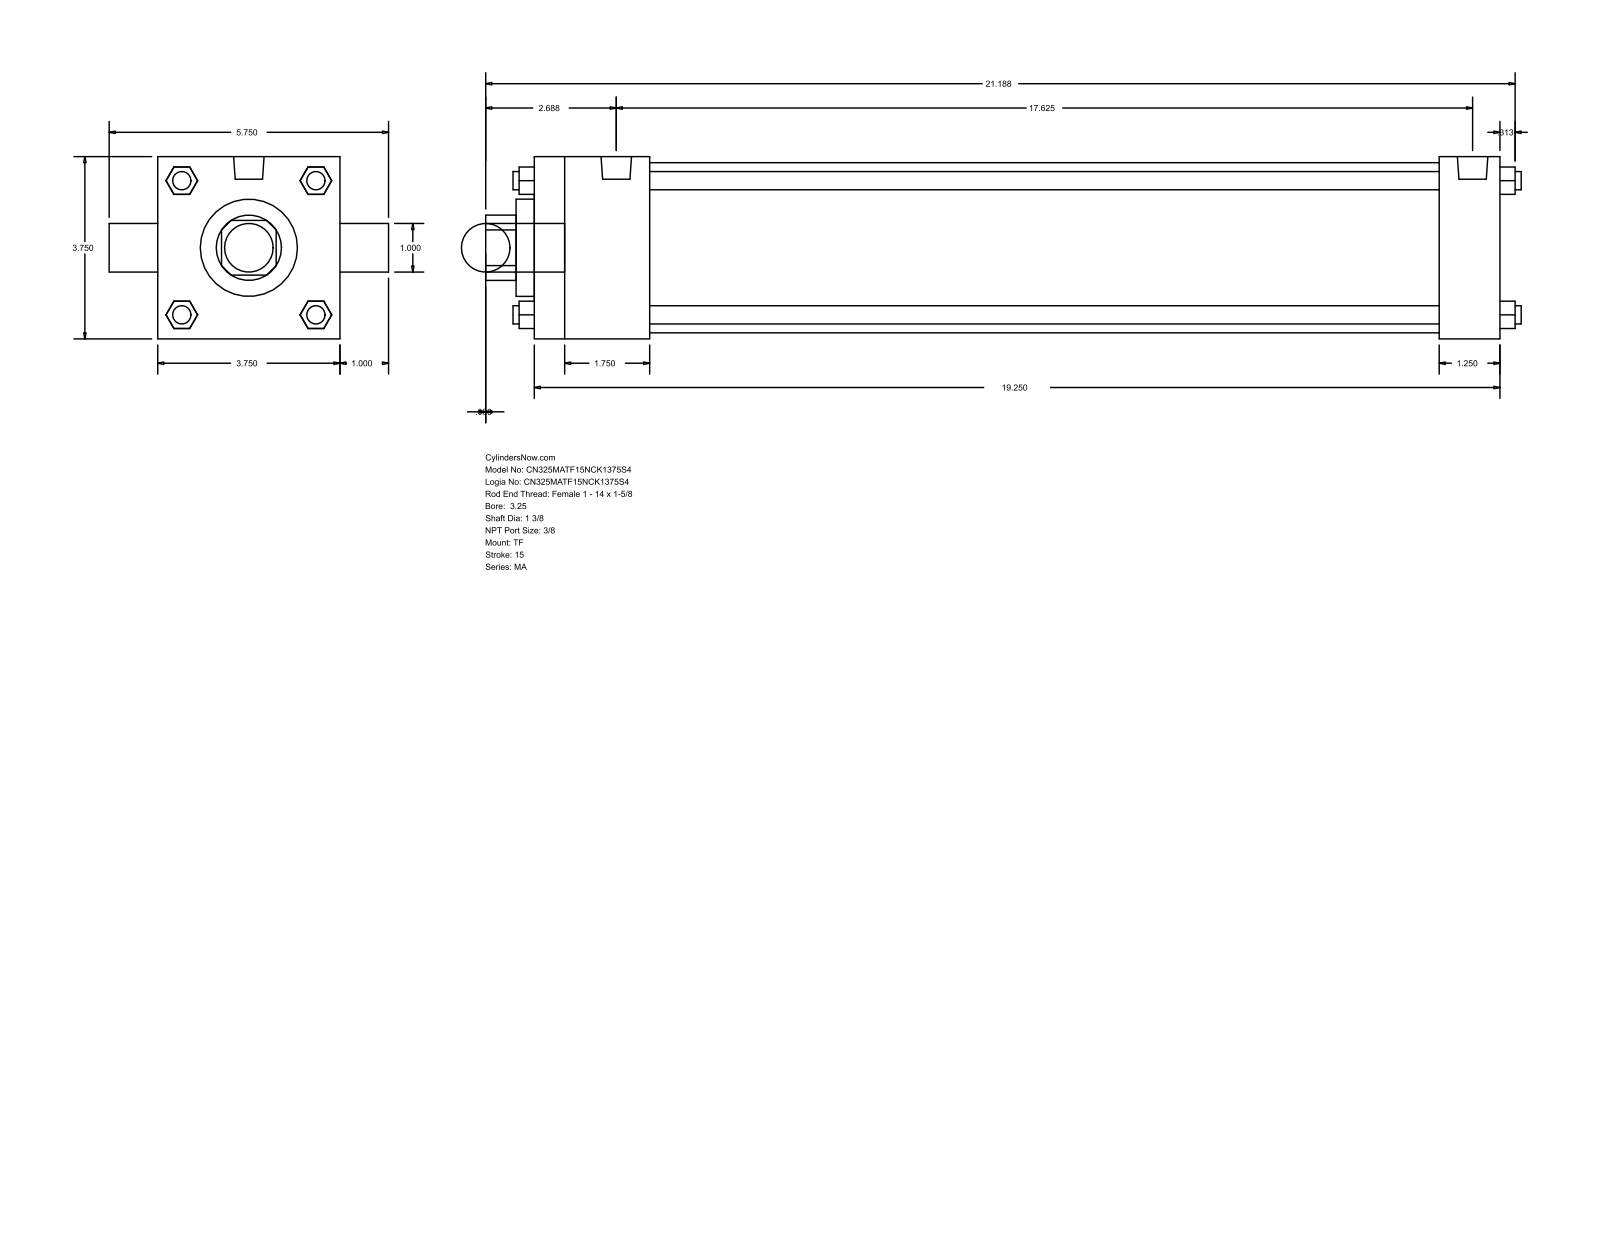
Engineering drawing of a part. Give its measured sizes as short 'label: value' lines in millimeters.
name: MA_TF__0325_1.375
written by: GSSL Pune (CONFIG_CONTROL_DESIGN)
unit: mm
bodies: 0 solids, 120 faces (92 planar, 28 cylindrical, 0 other)
size: 541.34 × 146.05 × 95.25
holes: 1× ⌀25.4, 1× ⌀34.92, 1× ⌀50.8, 1× ⌀88.9
bosses: 4× ⌀9.53, 3× ⌀11.11, 2× ⌀15.93, 1× ⌀25.4
rounds: 1× R17.06
face distances: 95.24, 504.83, 60.32, 473.08, 412.76, 444.51, 31.75, 9.52, 69.84, 482.6
